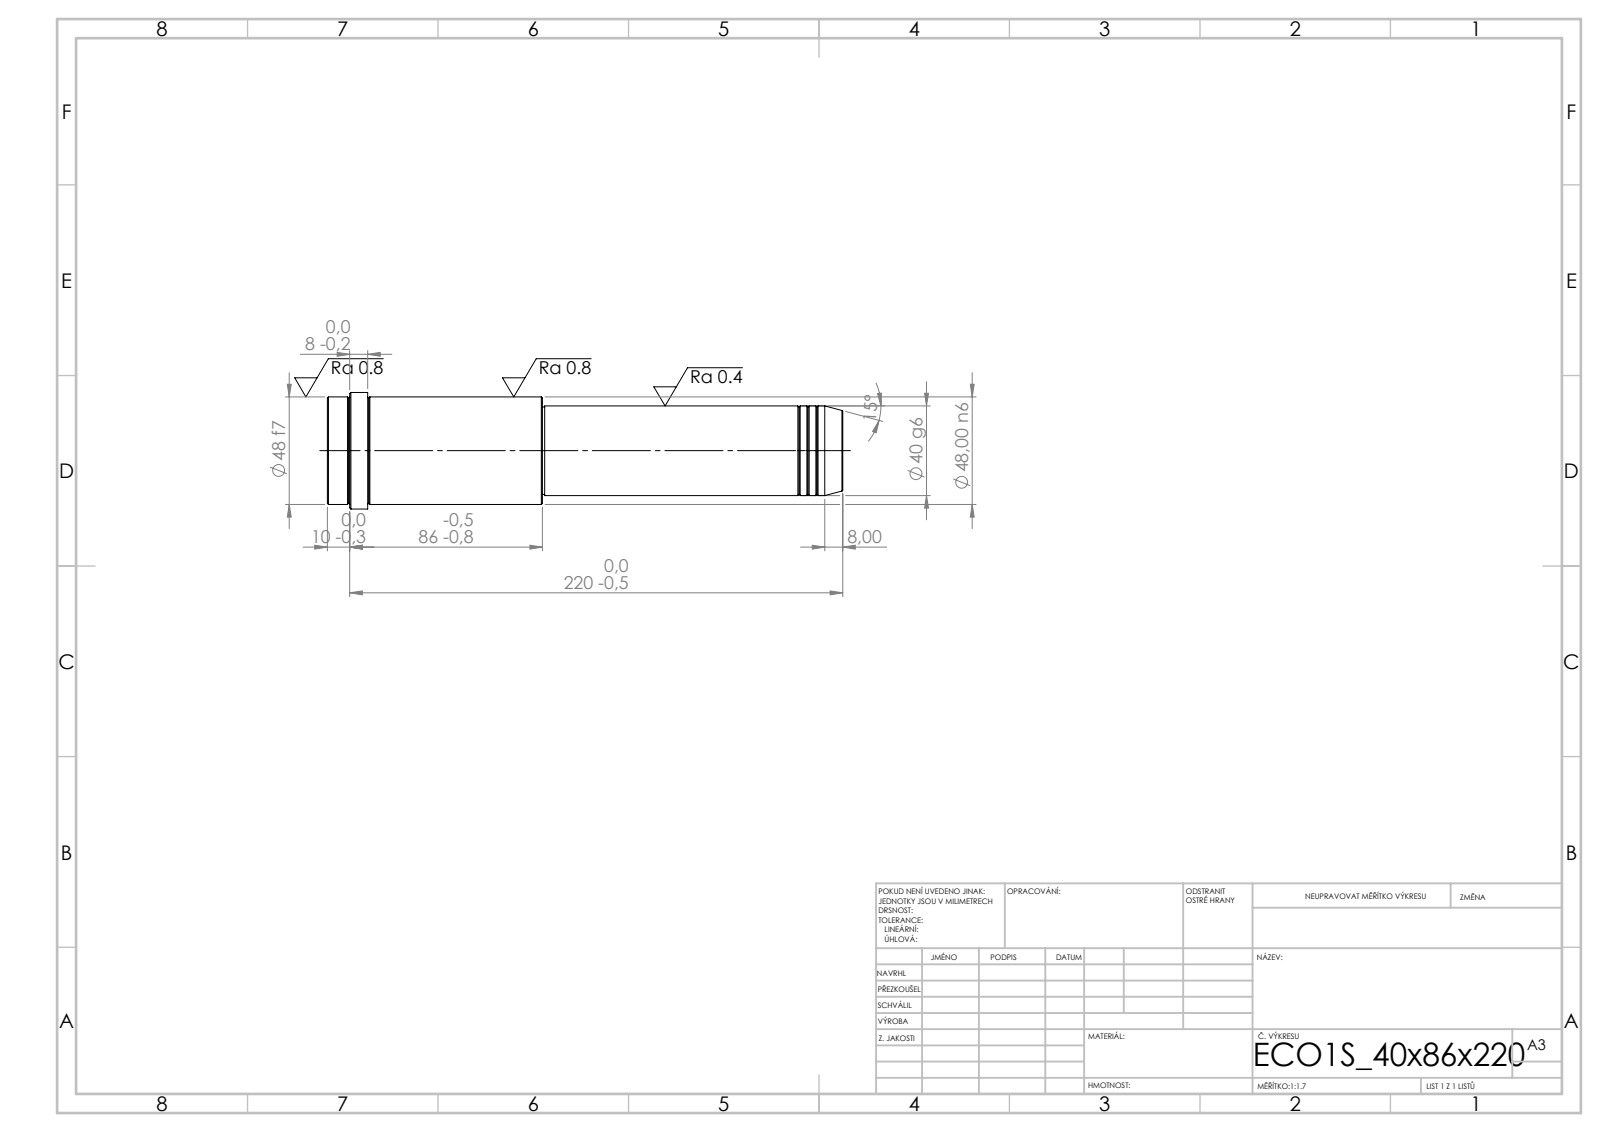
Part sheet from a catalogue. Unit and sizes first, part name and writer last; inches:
Units: inches
Overall size (bounding box): 9.055 × 2.047 × 2.047
Round bosses / shafts (diameter × count): ⌀2.047 ×1, ⌀1.89 ×1, ⌀1.575 ×1, ⌀1.535 ×1
Main face-to-face distances: 9.055, 5.276, 3.78, 8.346, 3.071, 0.709, 8.661, 3.386, 0.315, 0.394
Volume: 20.94 in³ · Surface area: 55.38 in²
Bodies: 1 solid, 52 faces (6 planar, 16 cylindrical, 30 other)
STEP written by: SolidWorks 2019 (CONFIG_CONTROL_DESIGN)
